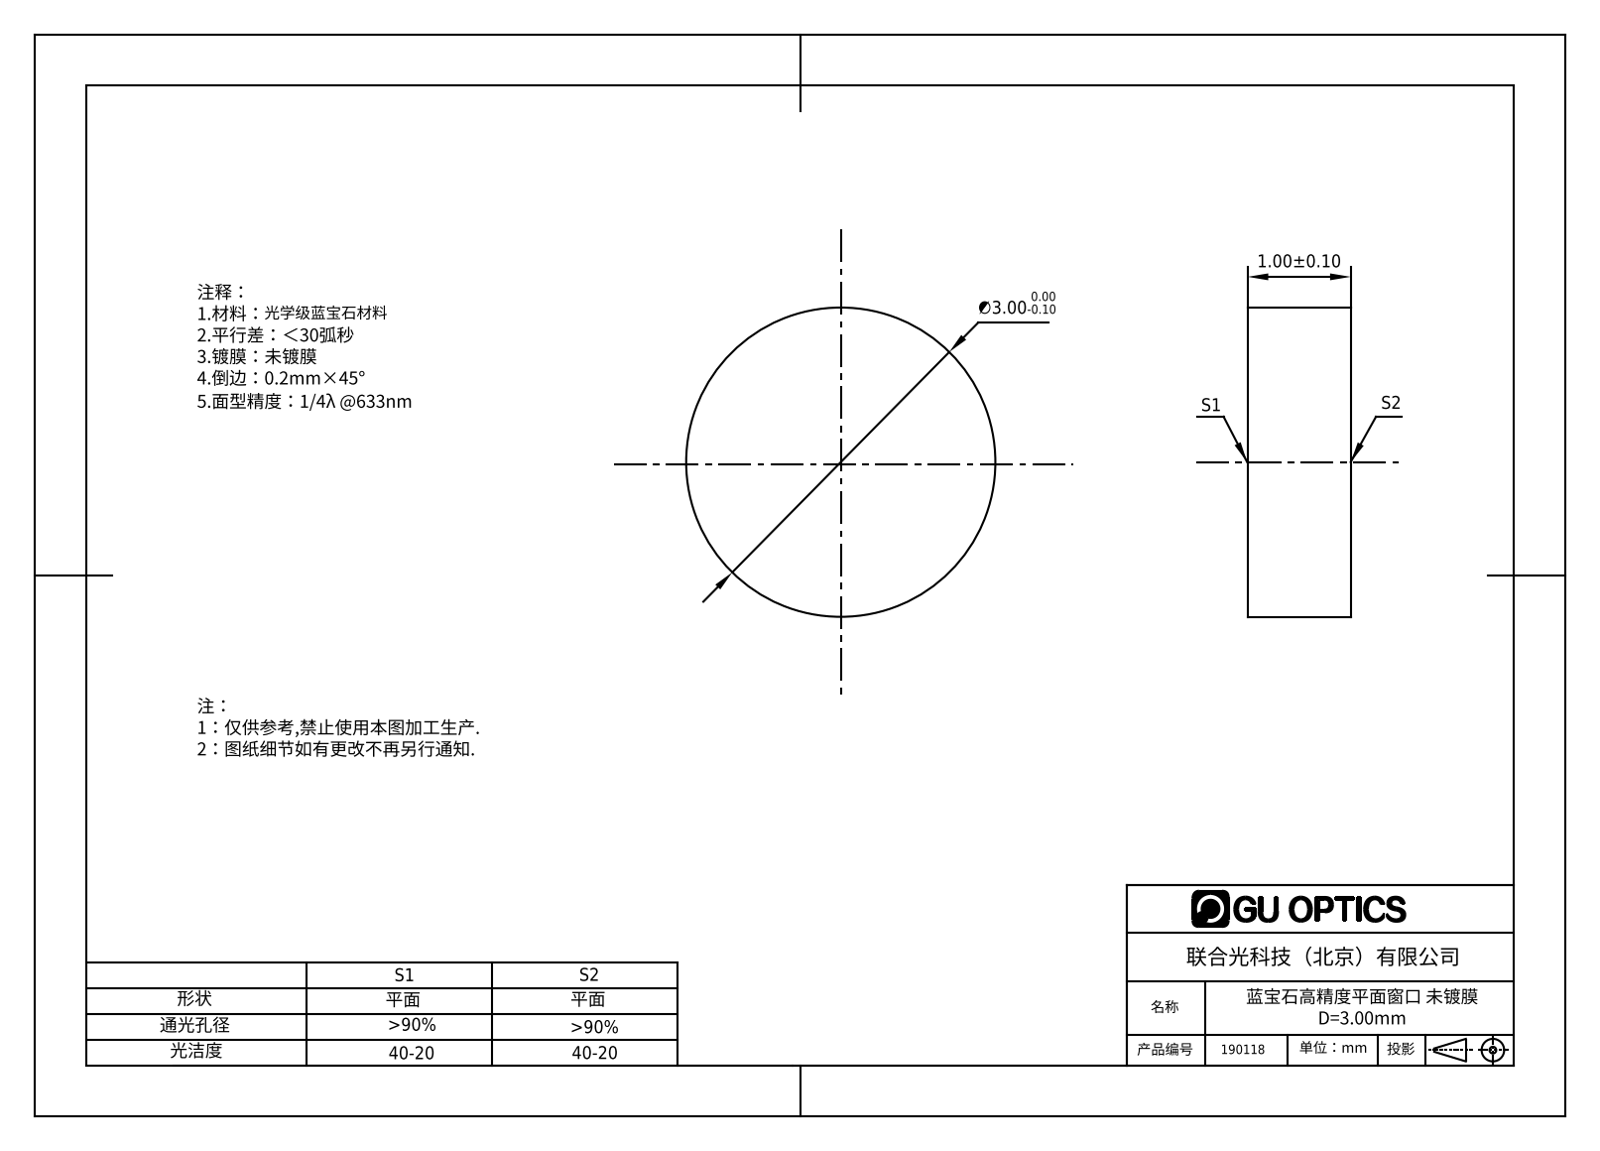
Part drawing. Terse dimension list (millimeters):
name: 190118
written by: SolidWorks 2016 (AUTOMOTIVE_DESIGN)
unit: mm
bodies: 1 solid, 4 faces (2 planar, 2 cylindrical, 0 other)
size: 3 × 3 × 1
volume: 7 mm³; area: 24 mm²
bosses: 1× ⌀3
face distances: 1
